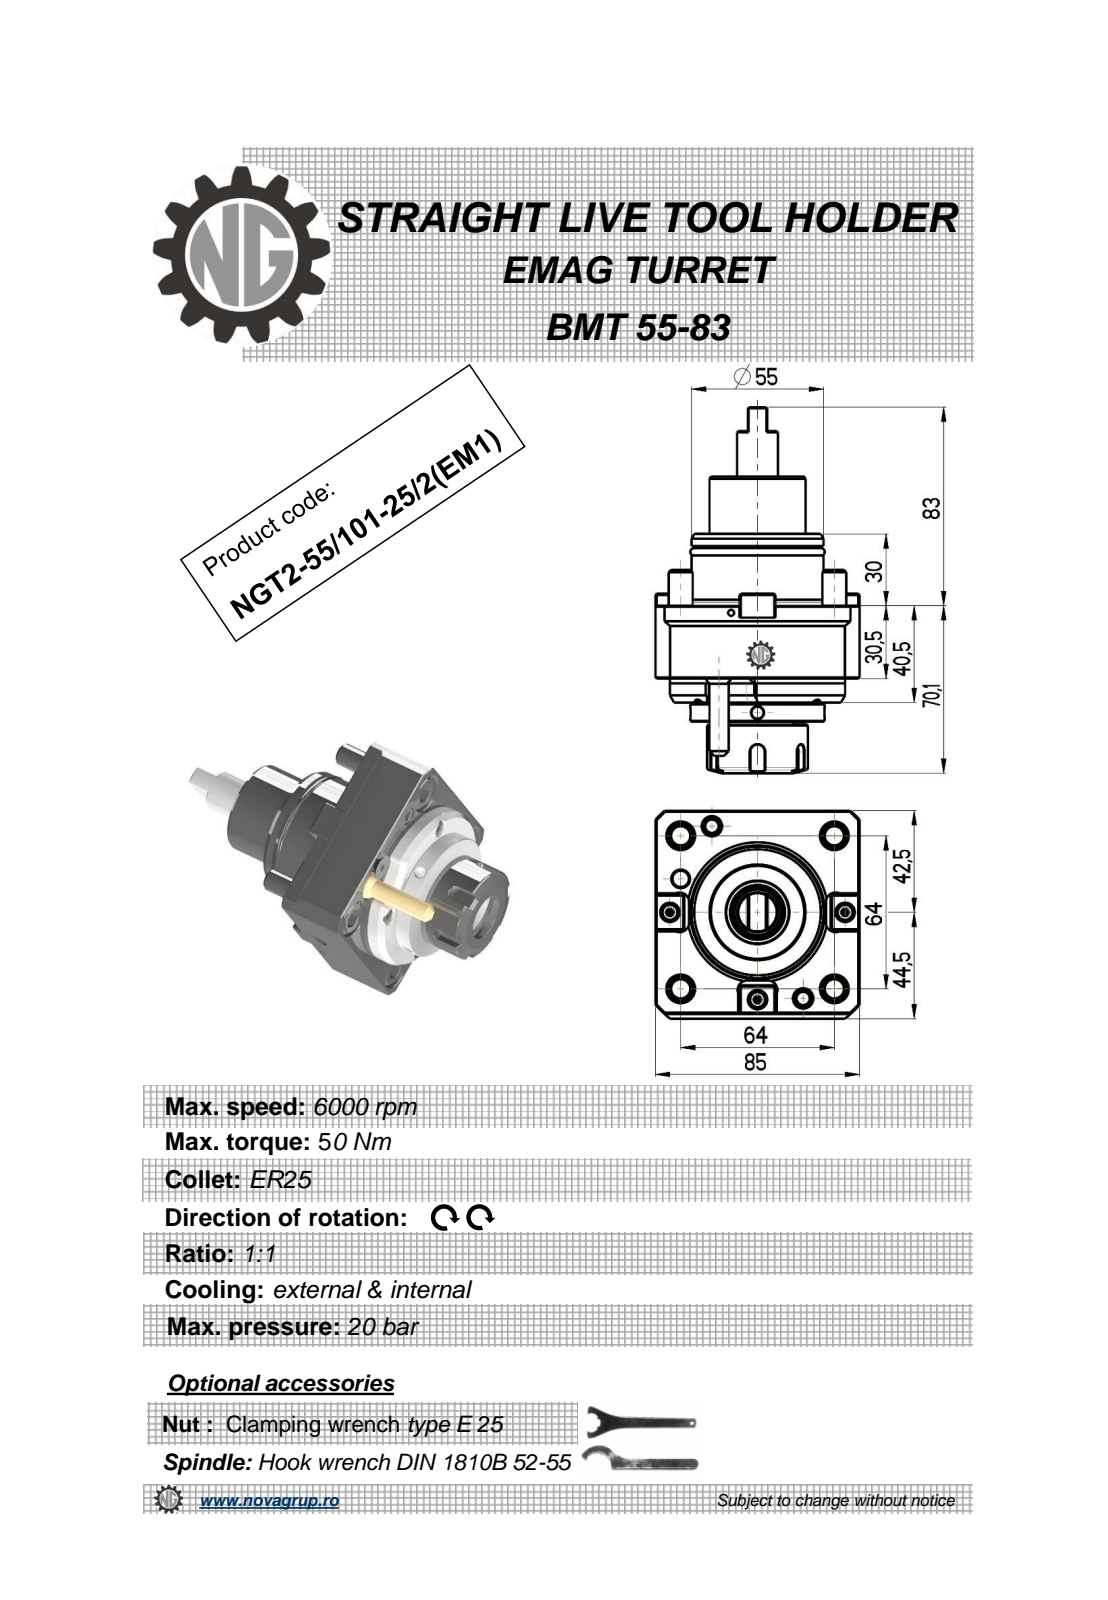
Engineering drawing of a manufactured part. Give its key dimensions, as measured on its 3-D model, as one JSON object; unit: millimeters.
{"part_name": "NGT2_55_101_25_1_EM1", "step_written_by": "PRO/ENGINEER BY PARAMETRIC TECHNOLOGY CORPORATION, 2010280 (CONFIG_CONTROL_DESIGN)", "units": "millimeters", "bodies": {"solids": 2, "faces": 318, "planar": 140, "cylindrical": 69, "other": 109}, "overall_size": [153.1, 87, 85], "volume_mm3": 422273, "surface_area_mm2": 50827, "round_holes": [[5, 3], [3, 1], [6.8, 1], [20.3, 1]], "round_bosses_or_shafts": [[10, 5], [73, 1], [56, 1], [55, 1], [54.4, 1], [50, 1], [43, 1], [42, 1]], "partial_cylinders_radius": [[0.2, 6], [3, 5], [0.8, 2], [6, 2], [57.5, 1]], "face_to_face_distances": [30.5, 85, 10, 40.5, 8, 48.5, 87, 18, 95, 10.5], "hole_center_spacings": [34.93, 37.12, 50.12]}
